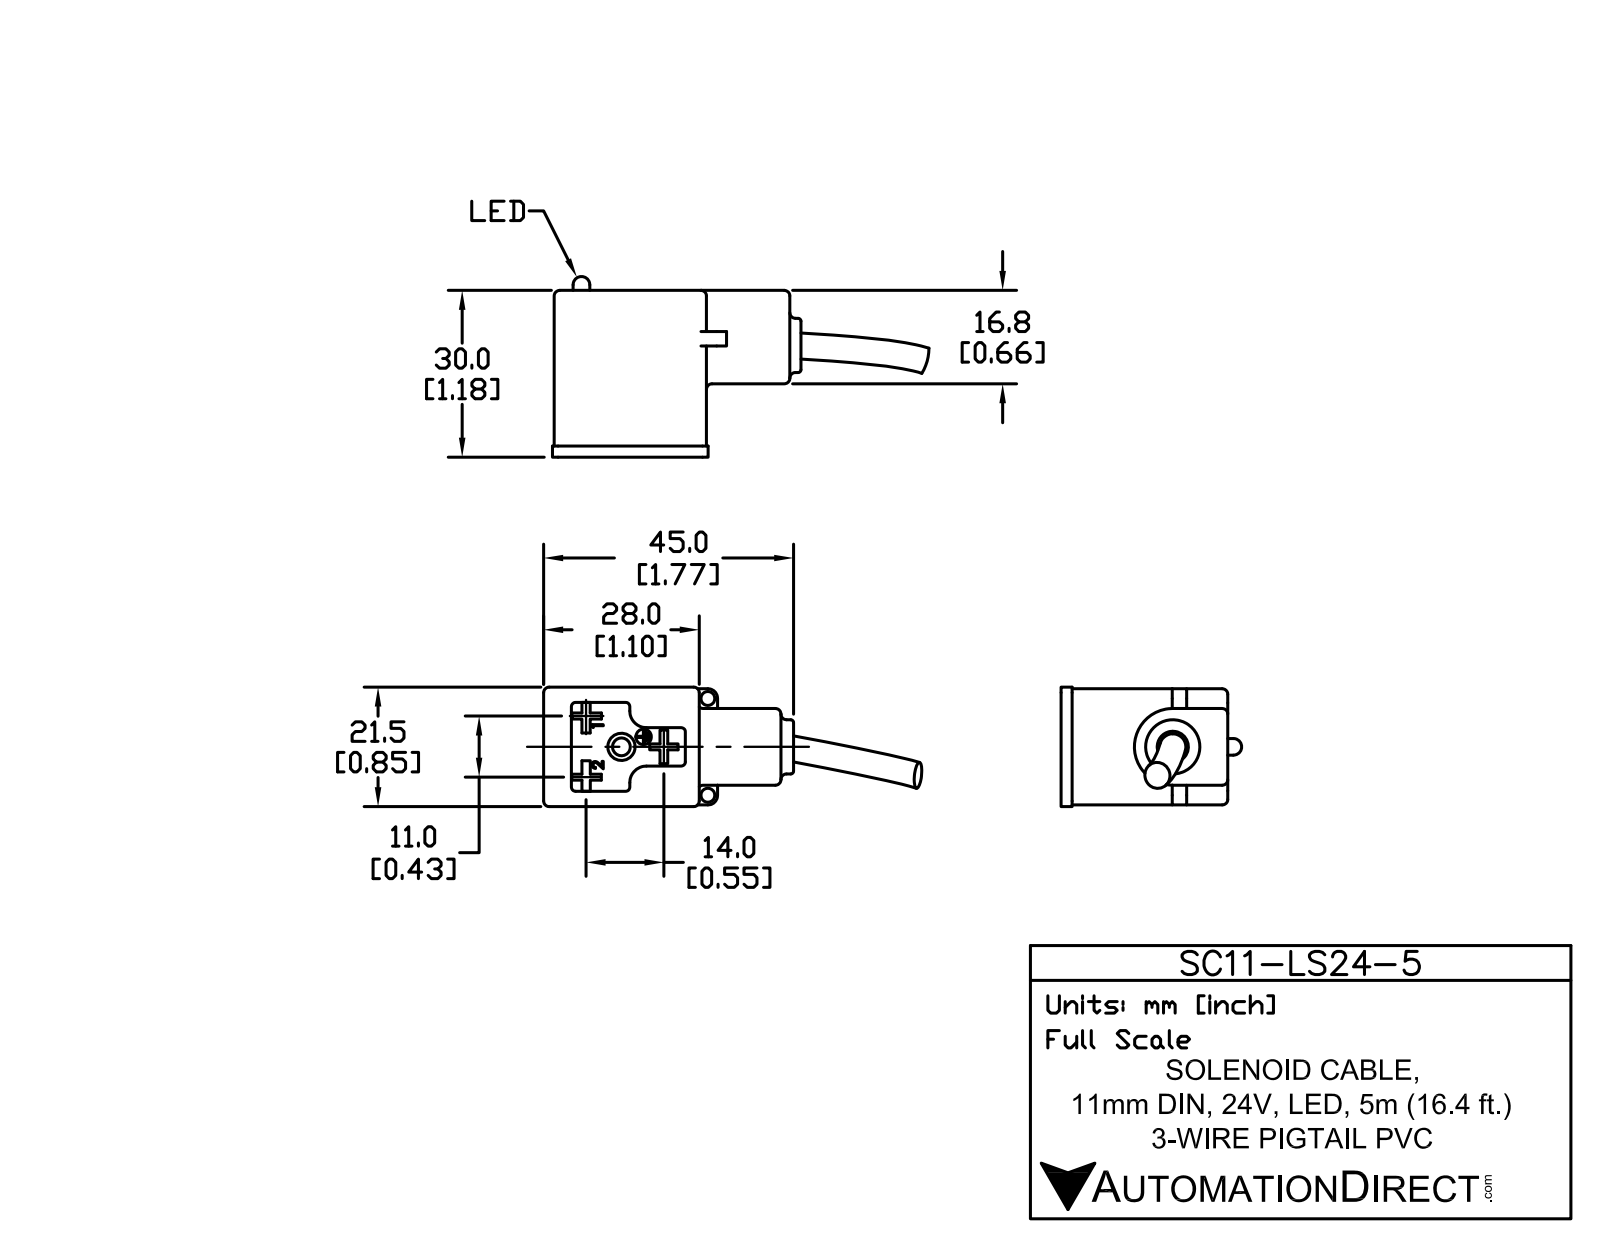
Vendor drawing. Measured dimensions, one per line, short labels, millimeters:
name: SC11-LS24-5
written by: SolidWorks 2011 (AUTOMOTIVE_DESIGN)
unit: mm
bodies: 3 solids, 205 faces (131 planar, 46 cylindrical, 28 other)
size: 67.77 × 36.8 × 21.5
volume: 20 000 mm³; area: 6 766 mm²
holes: 2× ⌀2.5, 1× ⌀2.78, 1× ⌀3.2, 1× ⌀4.9, 1× ⌀5.6, 1× ⌀6.6
bosses: 1× ⌀9.75, 1× ⌀6.5, 1× ⌀3, 1× ⌀2.75
rounds: 19× R1, 6× R0.75, 2× R1.75, 2× R3, 1× R6.9
face distances: 20.9, 30, 27.4, 28, 2, 3.55, 17.35, 27.95, 29.95, 13.8
hole spacings: 14.21, 17.82, 4.32, 17.4
